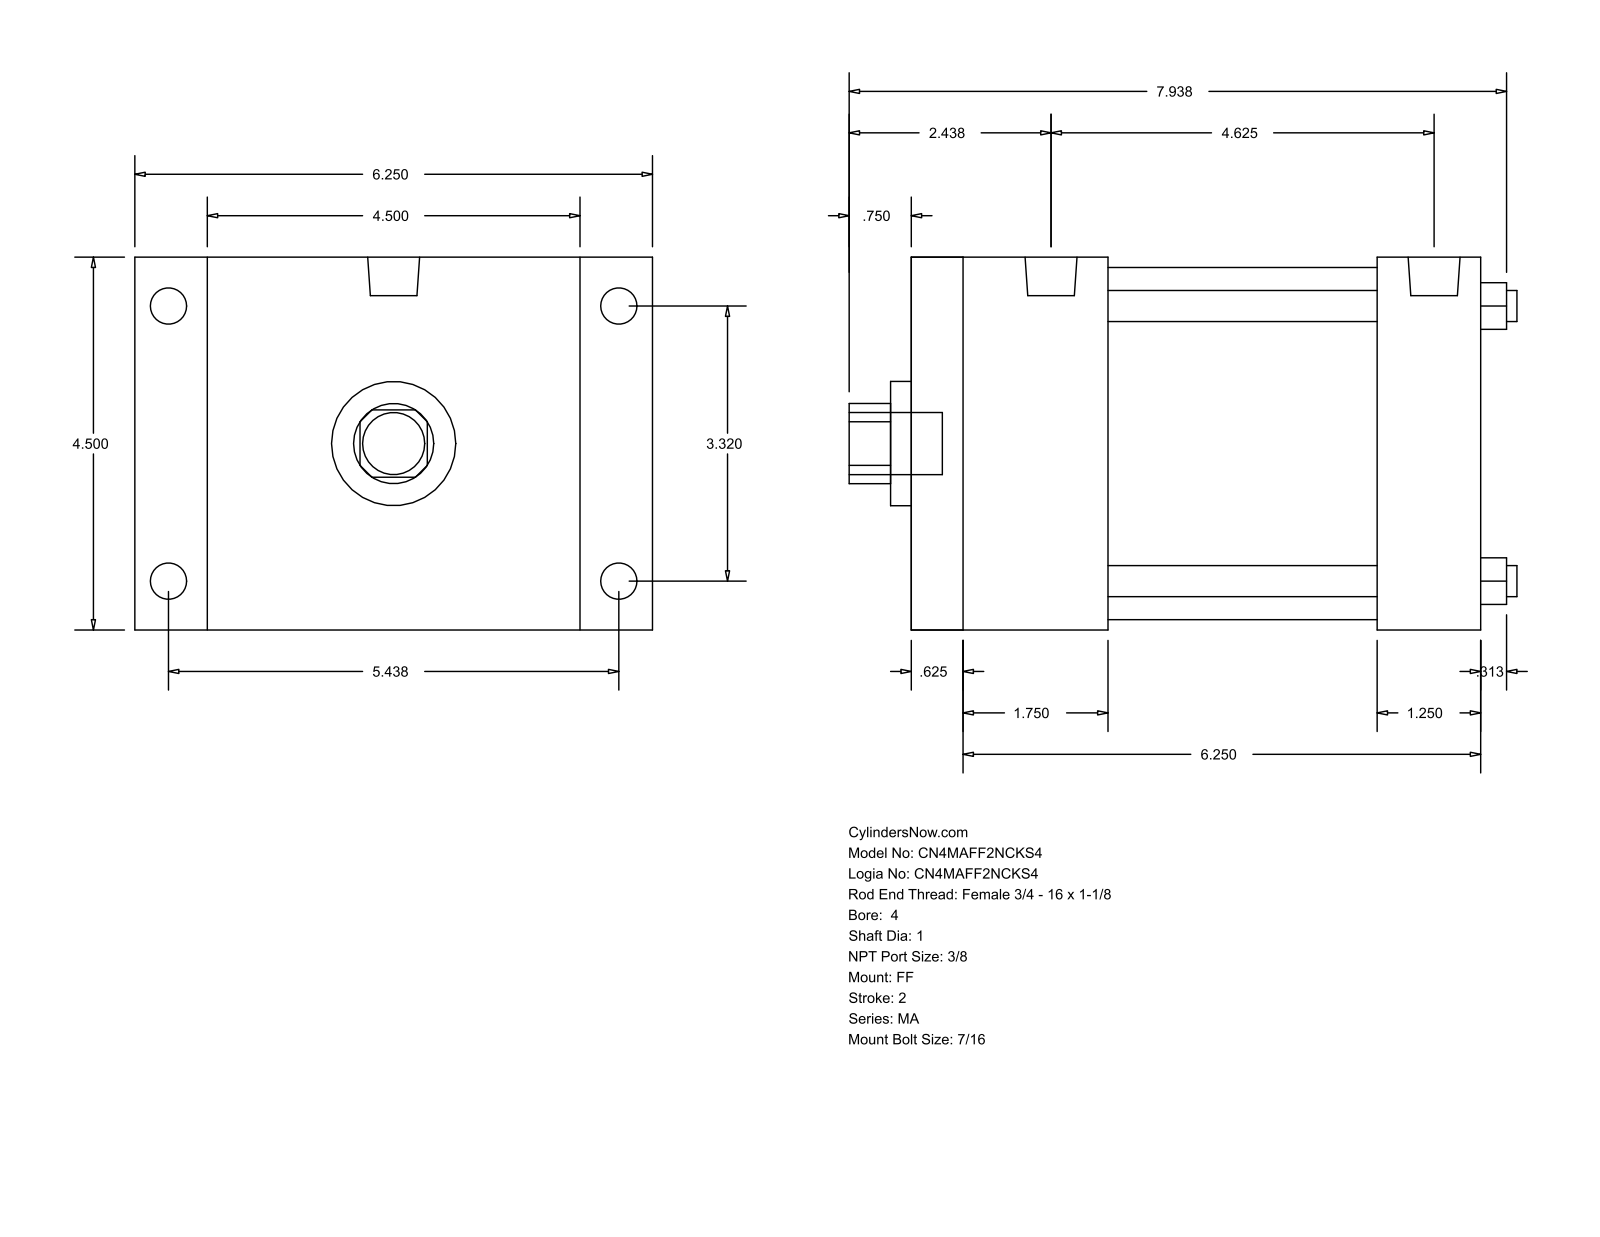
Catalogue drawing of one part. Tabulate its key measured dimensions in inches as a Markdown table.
| quantity | value |
| --- | --- |
| part name | MA_FF__0400_1 |
| STEP written by | GSSL Pune (CONFIG_CONTROL_DESIGN) |
| units | inches |
| bodies | 0 solids, 92 faces (64 planar, 28 cylindrical, 0 other) |
| overall size | 8.063 × 6.25 × 4.5 |
| round holes (diameter × count) | 0.375 × 4, 1 × 1, 1.5 × 1, 4.25 × 1 |
| round bosses / shafts (diameter × count) | 0.437 × 8, 0.627 × 2, 0.75 × 1 |
| partial cylindrical surfaces (radius × count) | 0.484 × 1 |
| main face-to-face distances | 4.5, 6.875, 6.25, 0.625, 0.875, 5.375, 5.625, 5, 1.25, 2.375 |
| hole center spacings | 2.347, 3.32, 4.695 |
